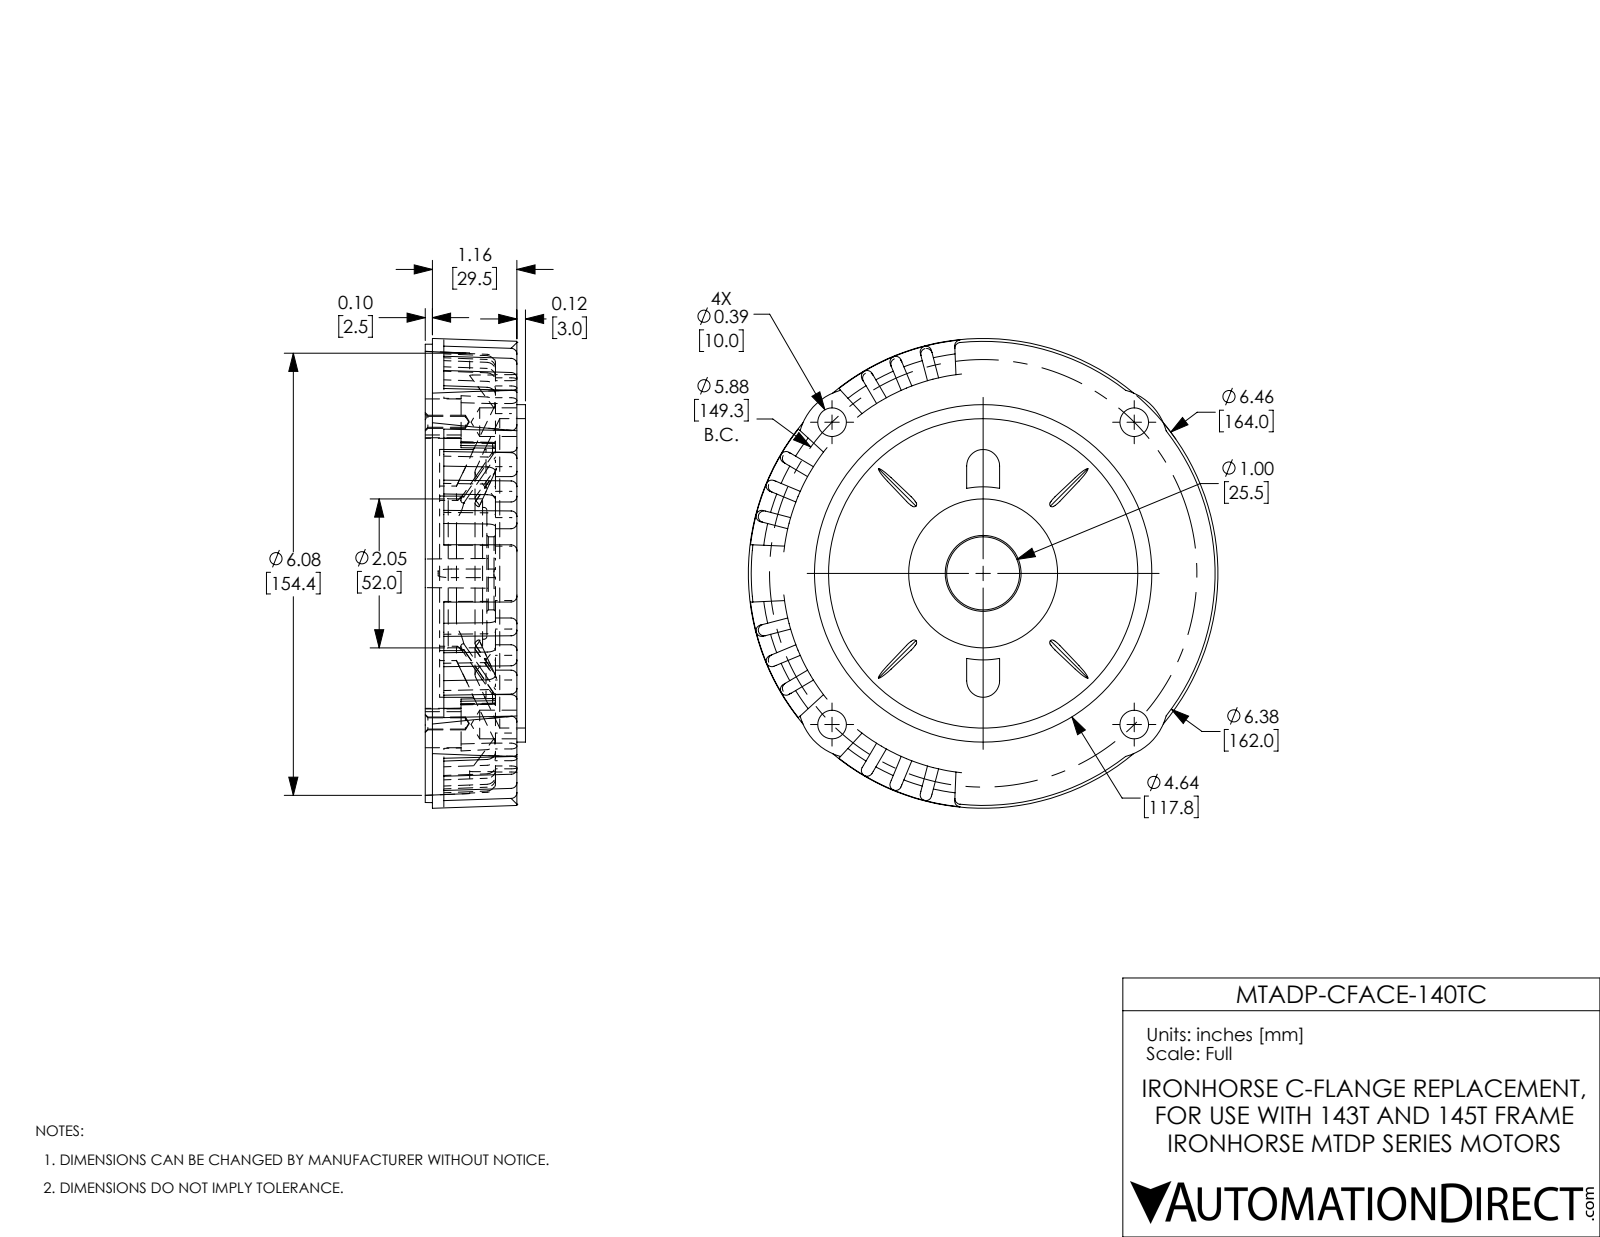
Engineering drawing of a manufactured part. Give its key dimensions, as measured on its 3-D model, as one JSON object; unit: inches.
{"part_name": "MTADP-CFACE-140", "step_written_by": "SolidWorks 2017 (AUTOMOTIVE_DESIGN)", "units": "inches", "bodies": {"solids": 1, "faces": 464, "planar": 142, "cylindrical": 176, "other": 146}, "overall_size": [6.457, 6.457, 1.378], "volume_in3": 11.88, "surface_area_in2": 130.8, "round_holes": [[0.165, 4], [0.394, 4], [1.004, 1], [1.811, 1], [2.047, 1], [4.252, 1]], "round_bosses_or_shafts": [[4.639, 1]], "partial_cylinders_radius": [[0.039, 38], [0.079, 32], [0.118, 16], [0.197, 6], [0.02, 4], [0.157, 4], [0.787, 4], [0.226, 2]], "face_to_face_distances": [0.295, 0.118, 0.413, 0.098, 0.768, 0.965, 1.26, 1.378, 0.591, 0.531], "hole_center_spacings": [2.938, 4.155, 5.871, 0.023, 2.933, 4.135, 4.167, 5.876]}
